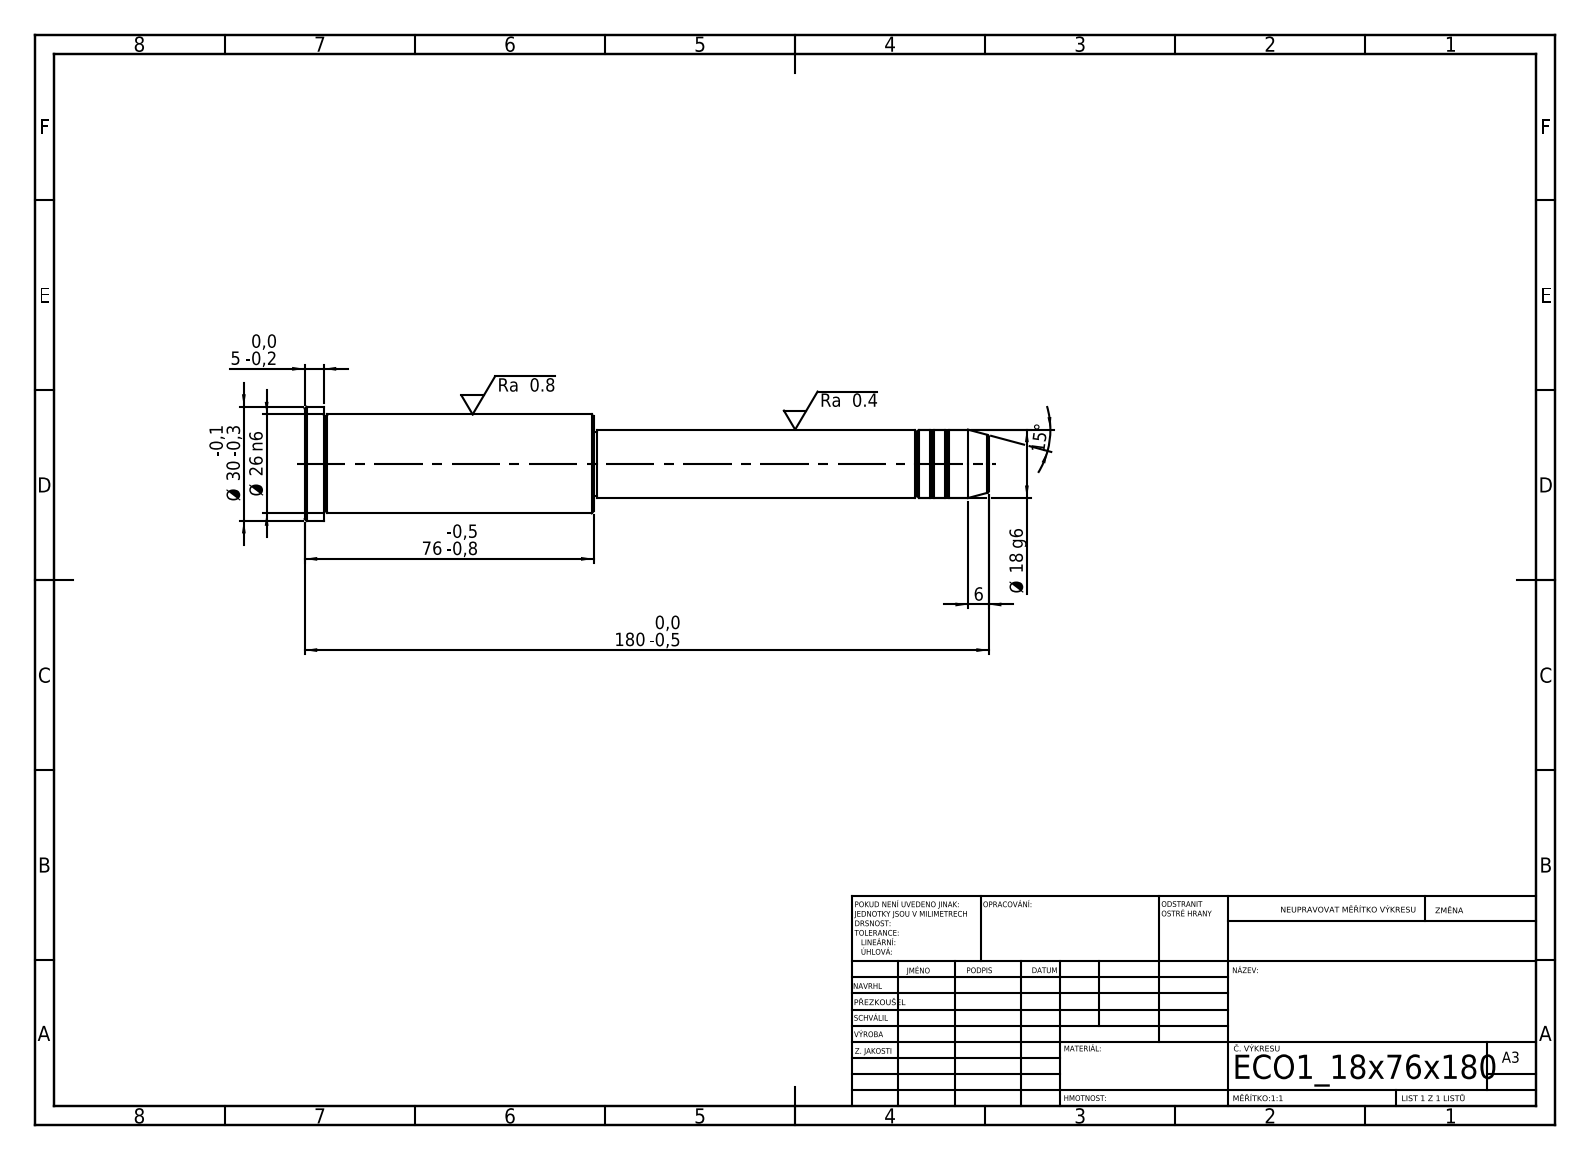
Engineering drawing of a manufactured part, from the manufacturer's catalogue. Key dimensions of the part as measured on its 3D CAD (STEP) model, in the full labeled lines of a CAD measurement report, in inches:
STEP written by: SolidWorks 2019 (CONFIG_CONTROL_DESIGN)
Units: inches
Bodies: 1 solid, 43 faces (5 planar, 14 cylindrical, 24 other)
Overall size (bounding box): 7.087 × 1.181 × 1.181
Volume: 4.109 in³ · Surface area: 21.08 in²
Round bosses / shafts (diameter × count): ⌀1.181 ×1, ⌀1.024 ×1, ⌀0.709 ×1, ⌀0.669 ×1
Main face-to-face distances: 2.992, 2.795, 0.197, 4.094, 6.89, 7.087, 4.055, 0.039, 2.835, 3.031
